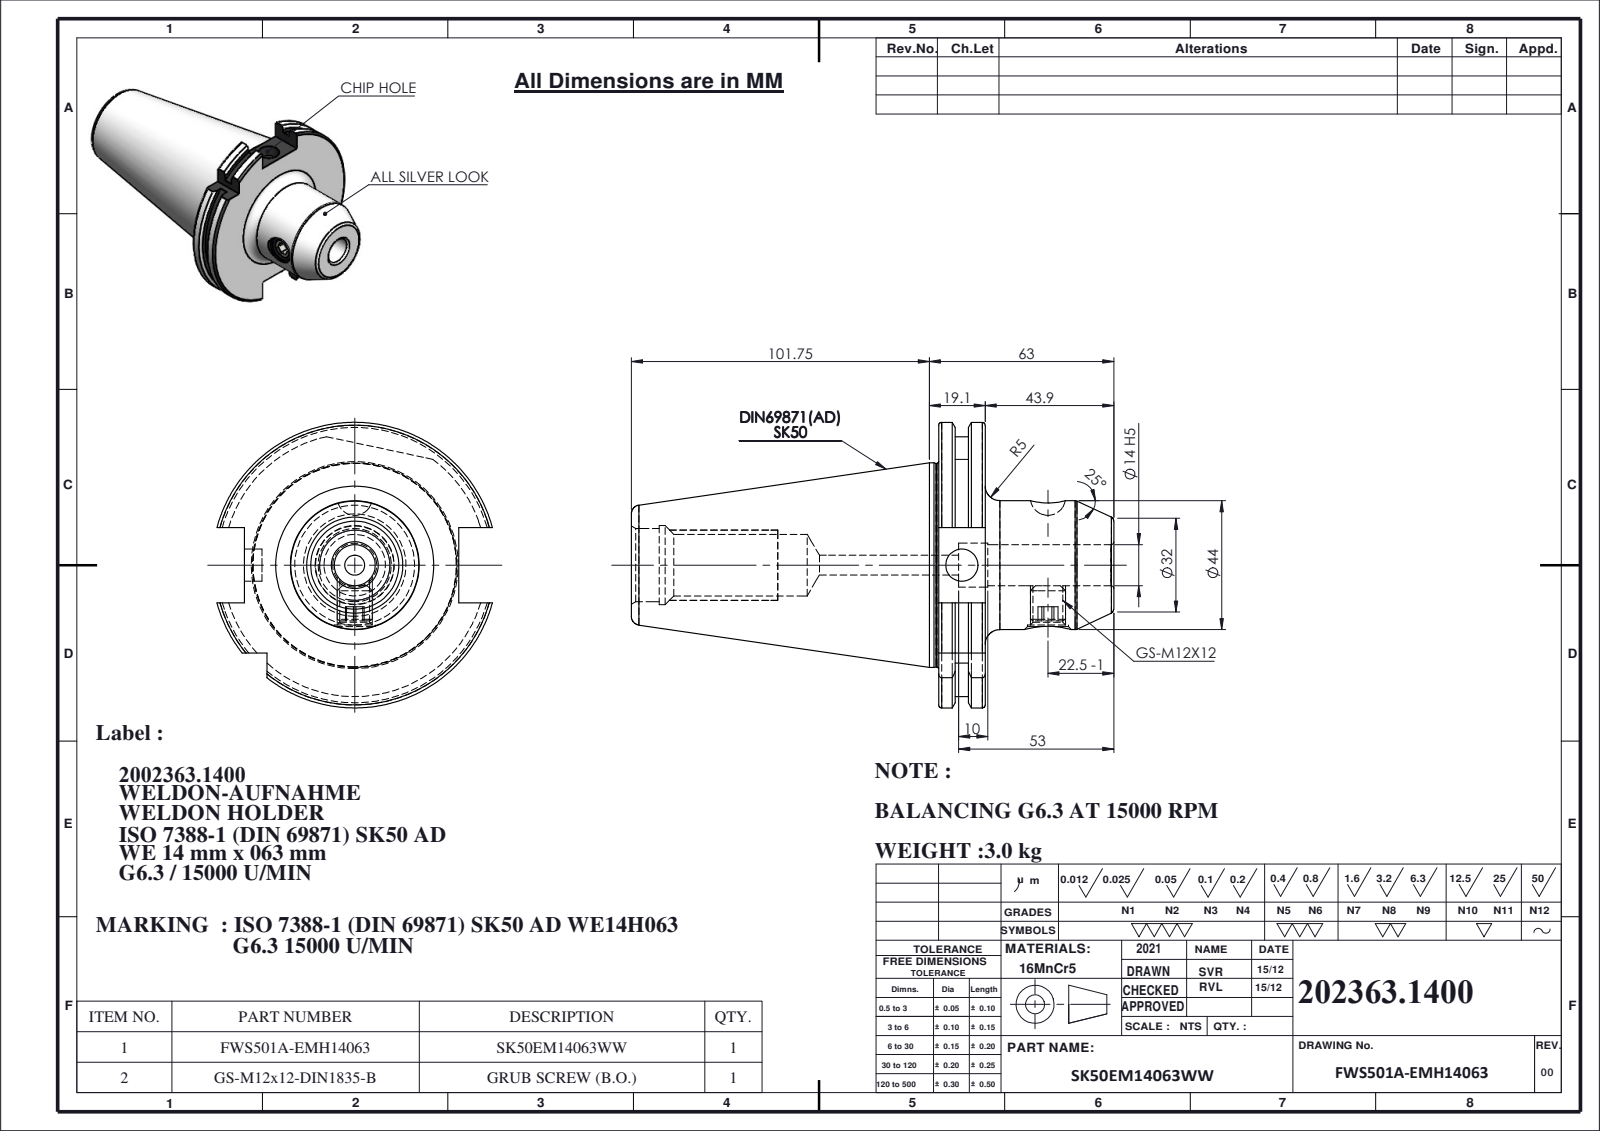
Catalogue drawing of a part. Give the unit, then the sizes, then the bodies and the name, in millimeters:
Units: millimetres
Overall size (bounding box): 164.75 × 97.5 × 94.05
Round holes (diameter × count): ⌀14 ×2, ⌀6.8 ×1, ⌀10.2 ×1, ⌀11 ×1, ⌀15 ×1, ⌀21 ×1, ⌀25 ×1, ⌀27 ×1
Round bosses / shafts (diameter × count): ⌀69.85 ×1, ⌀69.45 ×1, ⌀44 ×1, ⌀12 ×1
Partial cylindrical surfaces — rounded edges, fillets, slot ends (radius × count): R44.9 ×1, R48.75 ×1
Main face-to-face distances: 15.9, 5.65, 10.25, 10.14, 4.49, 5.76, 59.8, 54.15, 49.66, 43.9
Volume: 391 145 mm³ · Surface area: 50 039 mm²
Bodies: 2 solids, 125 faces (33 planar, 39 cylindrical, 53 other)
Part name (STEP PRODUCT): SK50EM14063WW; GS-M12X12-DIN1835-B_ISO 4026 - M12 x 12-N; 91506-WE114063; GS-M12X12-DIN1835-B
STEP written by: SolidWorks 2018 (CONFIG_CONTROL_DESIGN)
